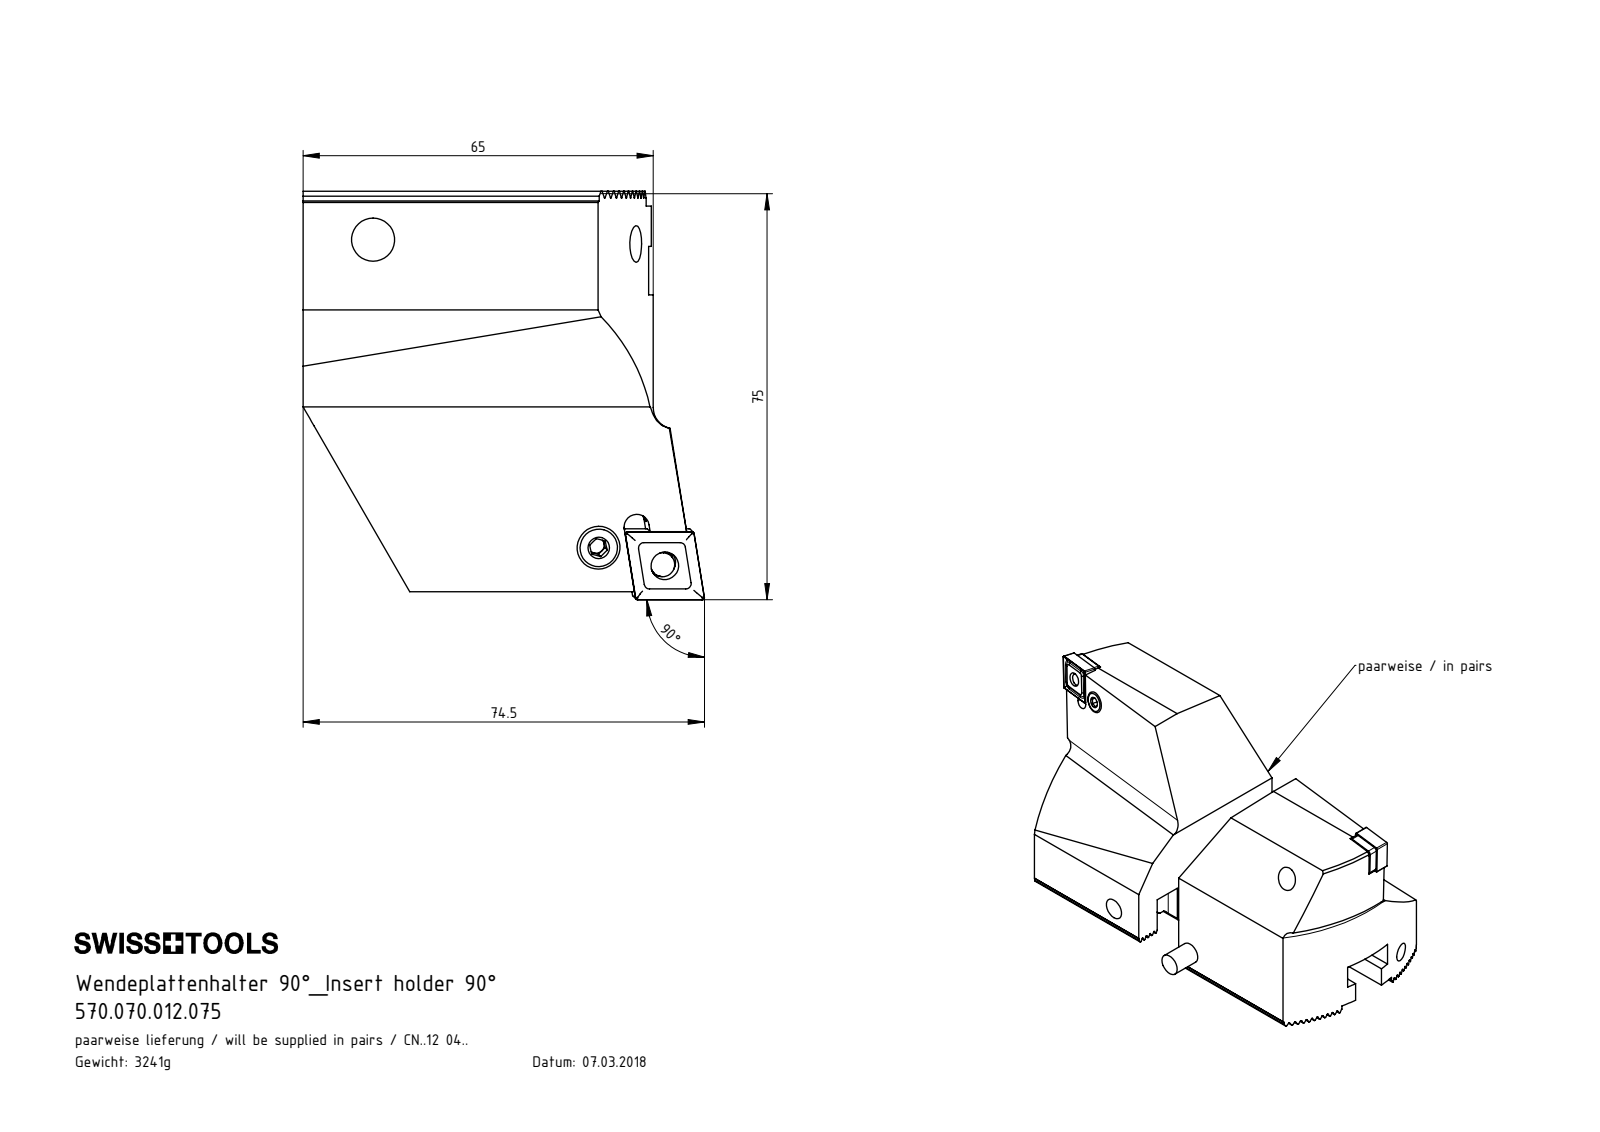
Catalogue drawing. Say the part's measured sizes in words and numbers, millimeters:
The part is named "VK1-WCD.101.075_A; WCD-ER1.101.000; ISO 8734 - 8 x 20 m6; ISO 4028 - M8 x 35 (+6 more)". Its 3-D file was written by "SolidWorks 2017 (CONFIG_CONTROL_DESIGN)". It is 16 solids with 1263 faces: 759 planar, 164 cylindrical and 340 other. Overall it measures 205.01 by 94 by 75.79 millimeters. Its volume is 413 723 cubic millimeters and its surface area 67 086 square millimeters. Round holes: 4 of diameter 8, 2 of diameter 5.16, 2 of diameter 6.4, 2 of diameter 6.8, 2 of diameter 7, 2 of diameter 8.4. Round bosses or shafts: 3 of diameter 8, 2 of diameter 7.9, 2 of diameter 6.4, 2 of diameter 4.5, 2 of diameter 3.55, 1 of diameter 5.5. Partial cylindrical surfaces (rounded edges, fillets, slot ends): 22 of radius 0.14, 8 of radius 0.4, 8 of radius 1, 6 of radius 2.5, 2 of radius 2.1, 2 of radius 2.2, 2 of radius 2.35, 2 of radius 2.8. The main face-to-face distances are 1.73, 8.66, 3.46, 70, 6.93, 5.2, 43.3, 24.5, 45.5, 10.39. The hole center spacings are 7, 12.8, 12.86, 75, 40, 68, 82.
